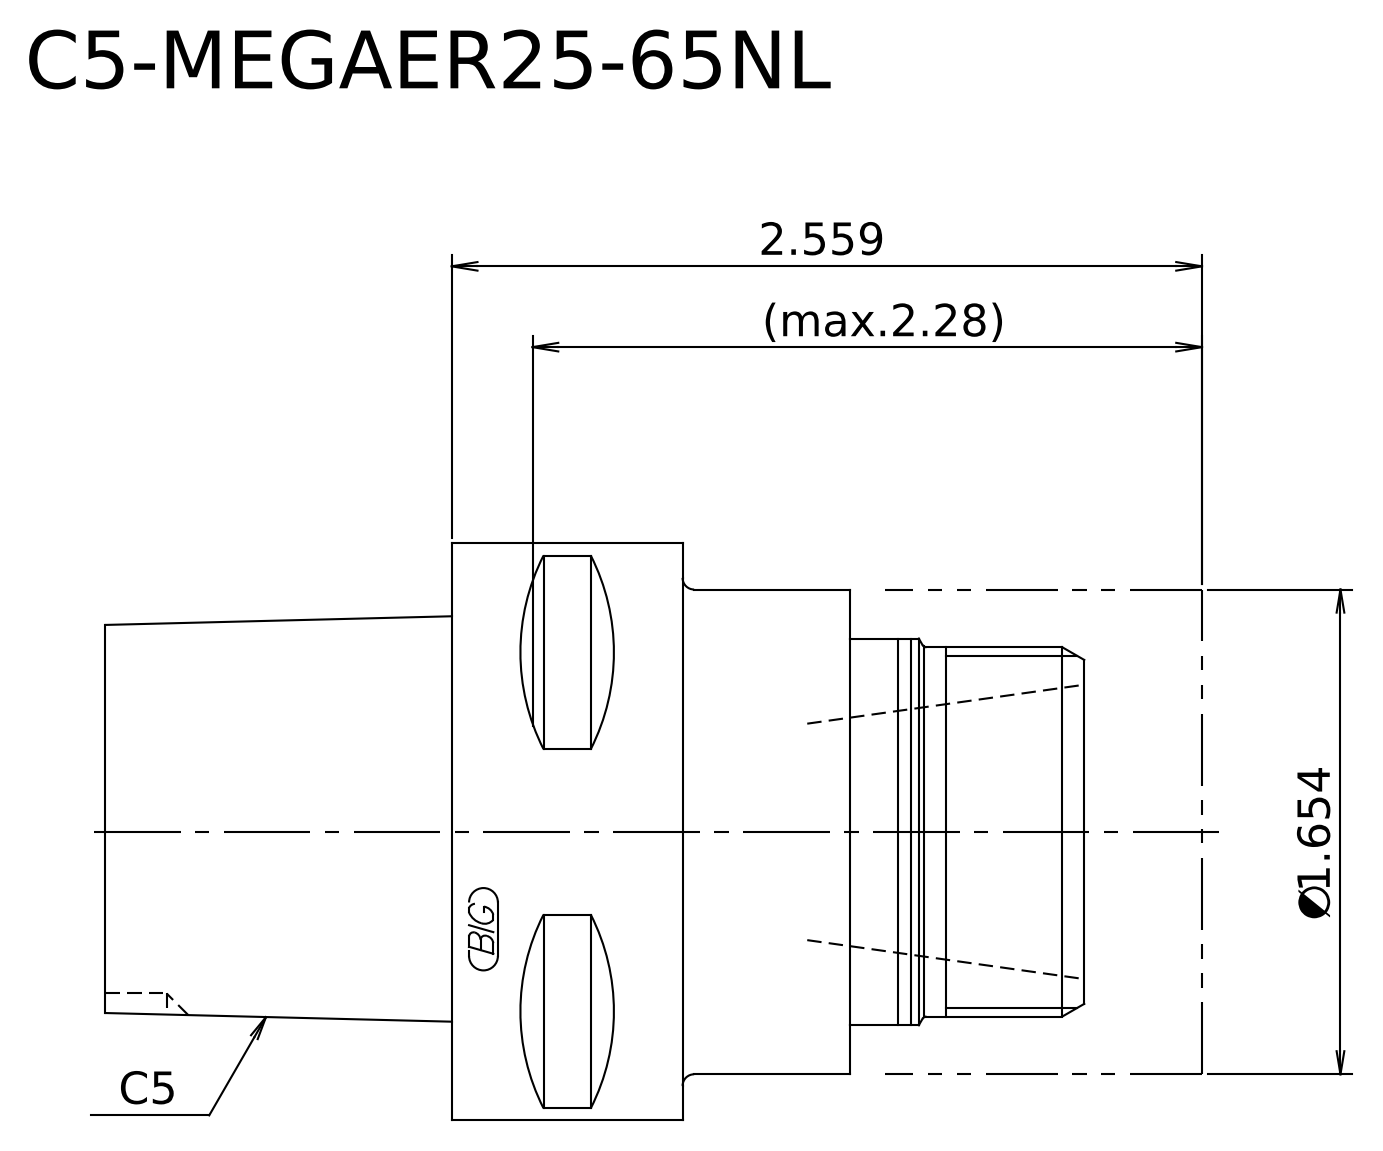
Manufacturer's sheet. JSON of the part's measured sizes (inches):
{"step_written_by": "Kubotek KeyCreator 2011 V10.0.2 (22737) (automotive_design)", "units": "inches", "bodies": {"solids": 2, "faces": 16, "planar": 7, "cylindrical": 5, "other": 4}, "overall_size": [3.74, 1.969, 1.969], "volume_in3": 8.629, "surface_area_in2": 31.65, "round_bosses_or_shafts": [[1.969, 1], [1.654, 1], [1.319, 1], [1.26, 1]], "face_to_face_distances": [1.083, 2.559, 1.476, 3.74, 2.657, 1.181, 0.402, 0.681, 2.157, 3.339]}
